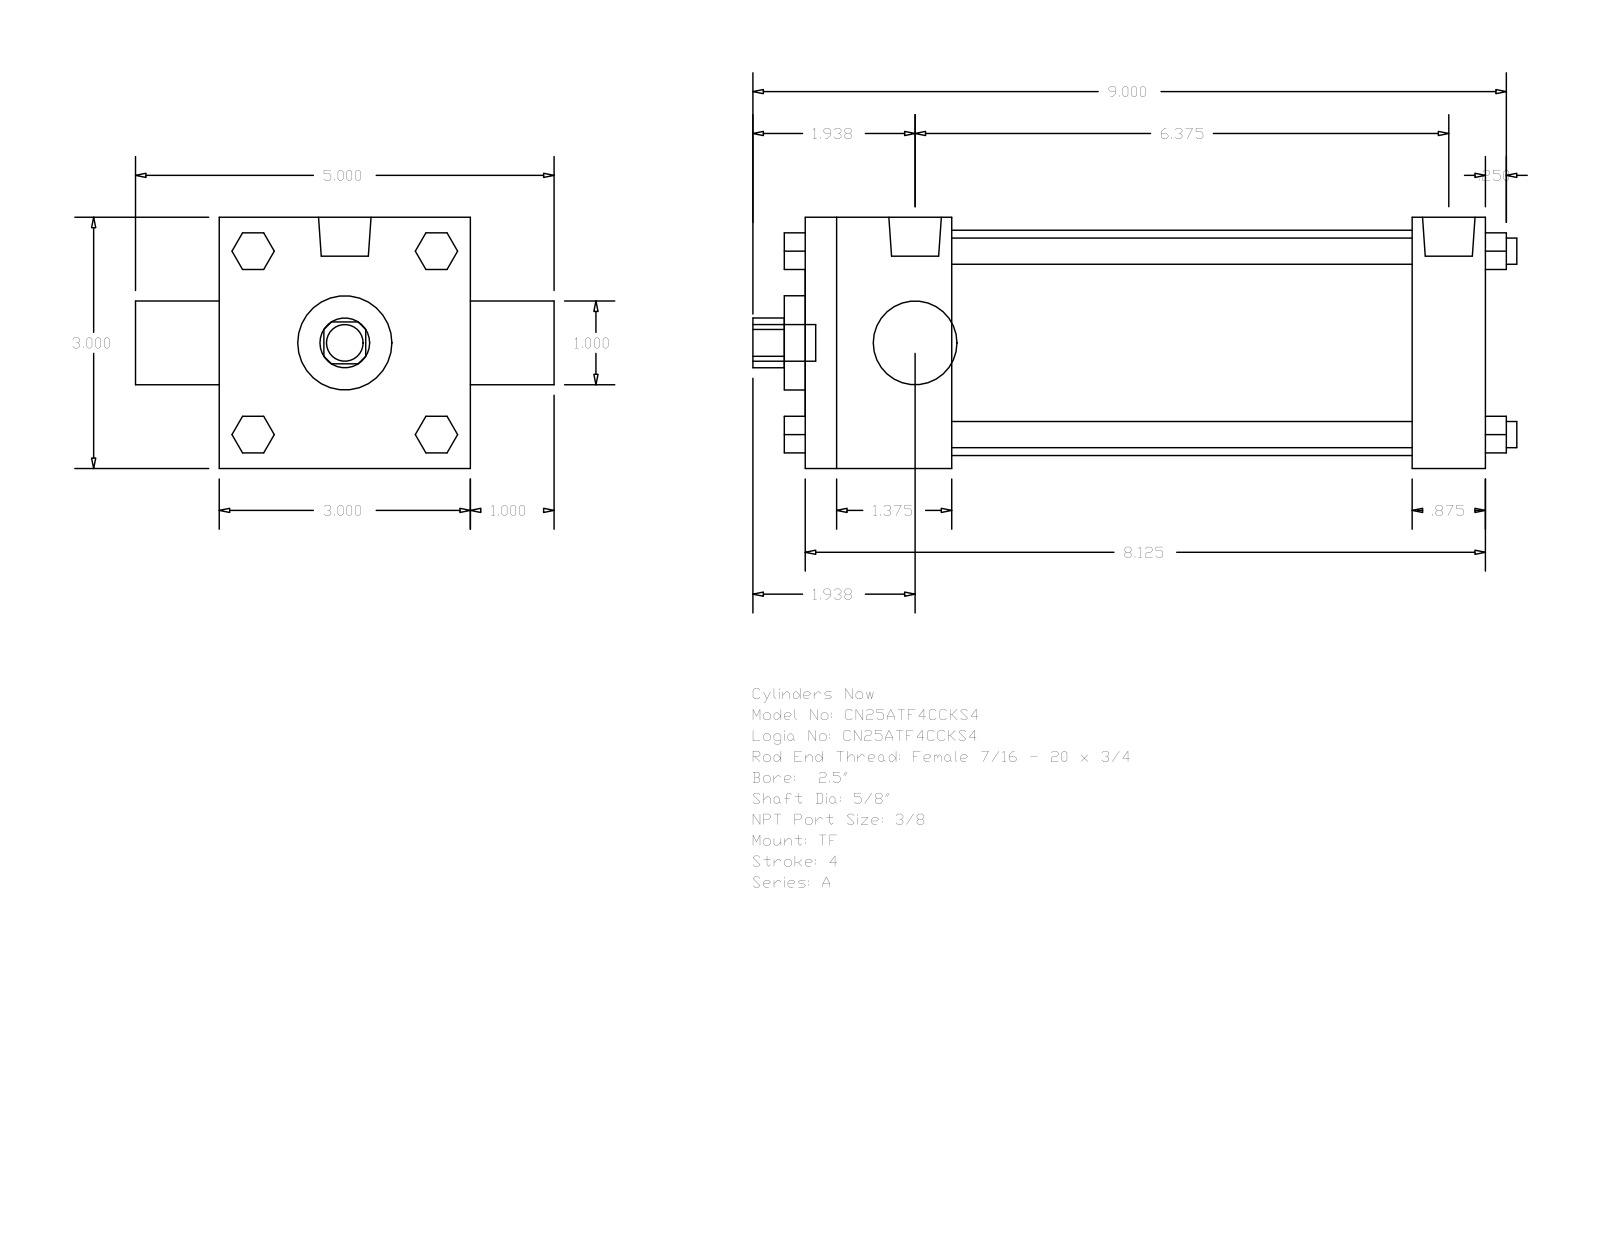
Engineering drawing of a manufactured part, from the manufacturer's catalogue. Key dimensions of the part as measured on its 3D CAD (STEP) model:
Part name (STEP PRODUCT): A_TF__0250_0.625
STEP written by: GSSL Pune (CONFIG_CONTROL_DESIGN)
Units: millimetres
Bodies: 0 solids, 120 faces (92 planar, 28 cylindrical, 0 other)
Overall size (bounding box): 231.78 × 127 × 76.2
Round holes (diameter × count): ⌀15.88 ×1, ⌀25.4 ×1, ⌀28.57 ×1, ⌀68.33 ×1
Round bosses / shafts (diameter × count): ⌀7.94 ×4, ⌀5.56 ×3, ⌀15.93 ×2, ⌀11.11 ×1
Partial cylindrical surfaces — rounded edges, fillets, slot ends (radius × count): R7.54 ×1
Main face-to-face distances: 76.2, 206.37, 44.45, 184.15, 139.7, 161.92, 22.22, 25.4, 101.6, 6.35
